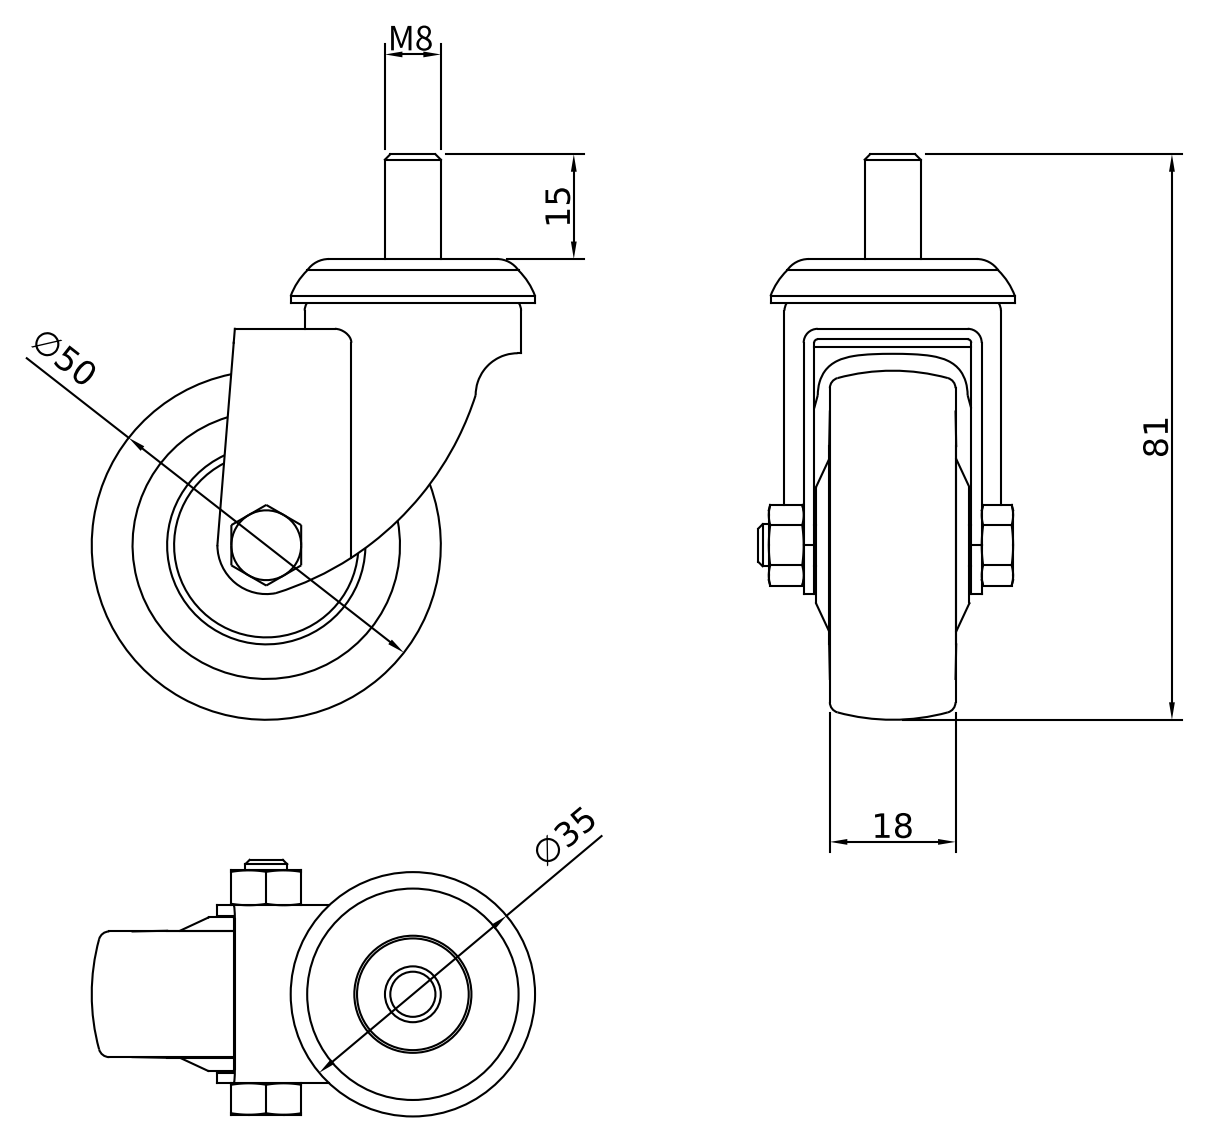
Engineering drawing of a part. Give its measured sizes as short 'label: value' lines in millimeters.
name: CRUST0000018; 440000025795; 440000025796; 440000025797 (+3 more)
written by: Autodesk Inventor 2022 (AUTOMOTIVE_DESIGN)
unit: mm
bodies: 7 solids, 144 faces (48 planar, 33 cylindrical, 63 other)
size: 81 × 63.5 × 36.75
volume: 44 130 mm³; area: 21 920 mm²
holes: 1× ⌀4.92, 1× ⌀6, 1× ⌀6.3, 1× ⌀8, 1× ⌀25.4, 1× ⌀28, 1× ⌀28.4
bosses: 1× ⌀35, 1× ⌀31, 1× ⌀26.4, 1× ⌀16, 1× ⌀8, 1× ⌀7.9, 1× ⌀7.1, 1× ⌀5.9
rounds: 2× R0.5, 2× R2, 1× R6, 1× R7, 1× R43.67
face distances: 1.5, 2.25, 21.75, 24, 3.75, 20.25, 25.5, 22.5, 23.25, 0.75
